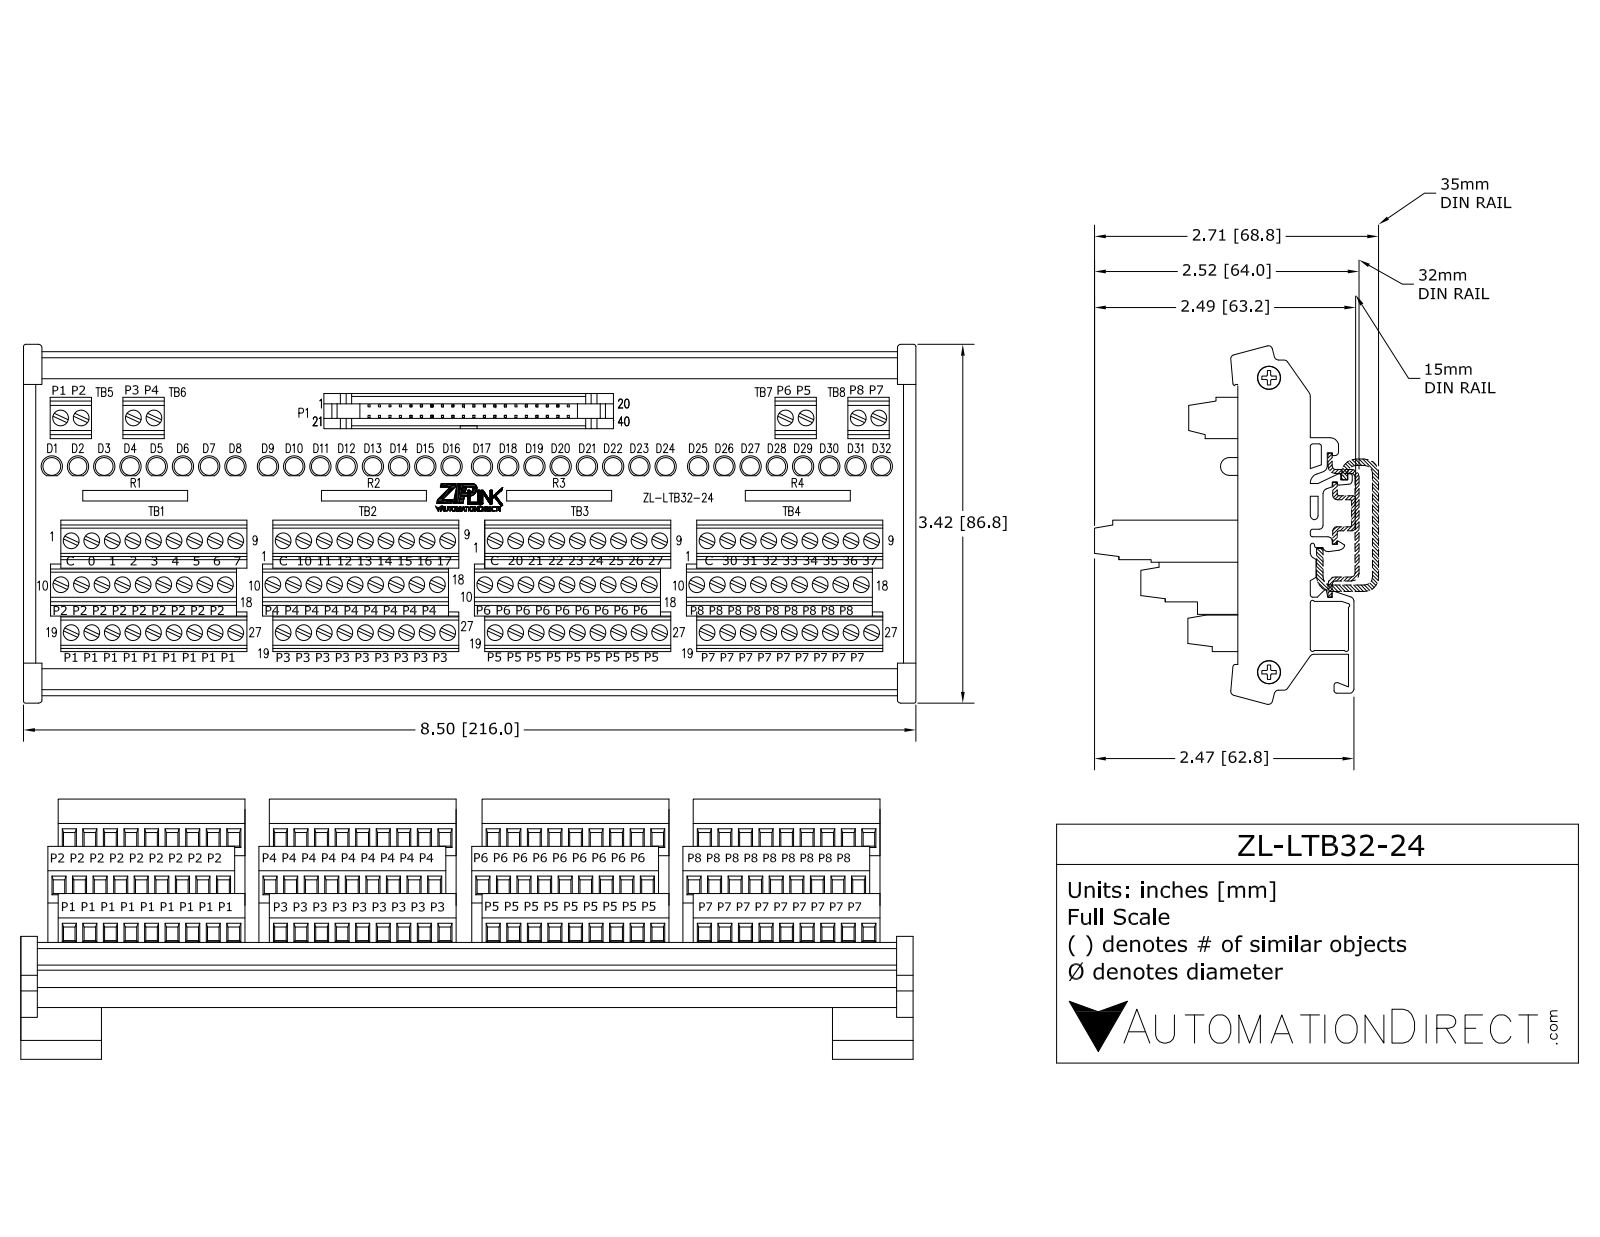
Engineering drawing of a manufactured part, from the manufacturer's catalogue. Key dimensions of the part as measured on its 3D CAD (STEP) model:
Part name (STEP PRODUCT): ZL-LTB32-24
STEP written by: SolidWorks 2014 (AUTOMOTIVE_DESIGN)
Units: inches
Bodies: 1 solid, 2785 faces (2186 planar, 453 cylindrical, 146 other)
Overall size (bounding box): 8.556 × 3.42 × 2.48
Volume: 15.71 in³ · Surface area: 192.9 in²
Round holes (diameter × count): ⌀0.15 ×116, ⌀0.225 ×2
Round bosses / shafts (diameter × count): ⌀0.03 ×40, ⌀0.205 ×2
Partial cylindrical surfaces — rounded edges, fillets, slot ends (radius × count): R0.015 ×41, R0.03 ×19, R0.06 ×4
Main face-to-face distances: 0.434, 0.137, 0.571, 0.628, 0.491, 0.057, 0.03, 2.03, 0.658, 0.52
Hole centre spacings: 0.196, 0.828, 0.392, 0.784, 0.98, 0.895, 1.123, 0.383
